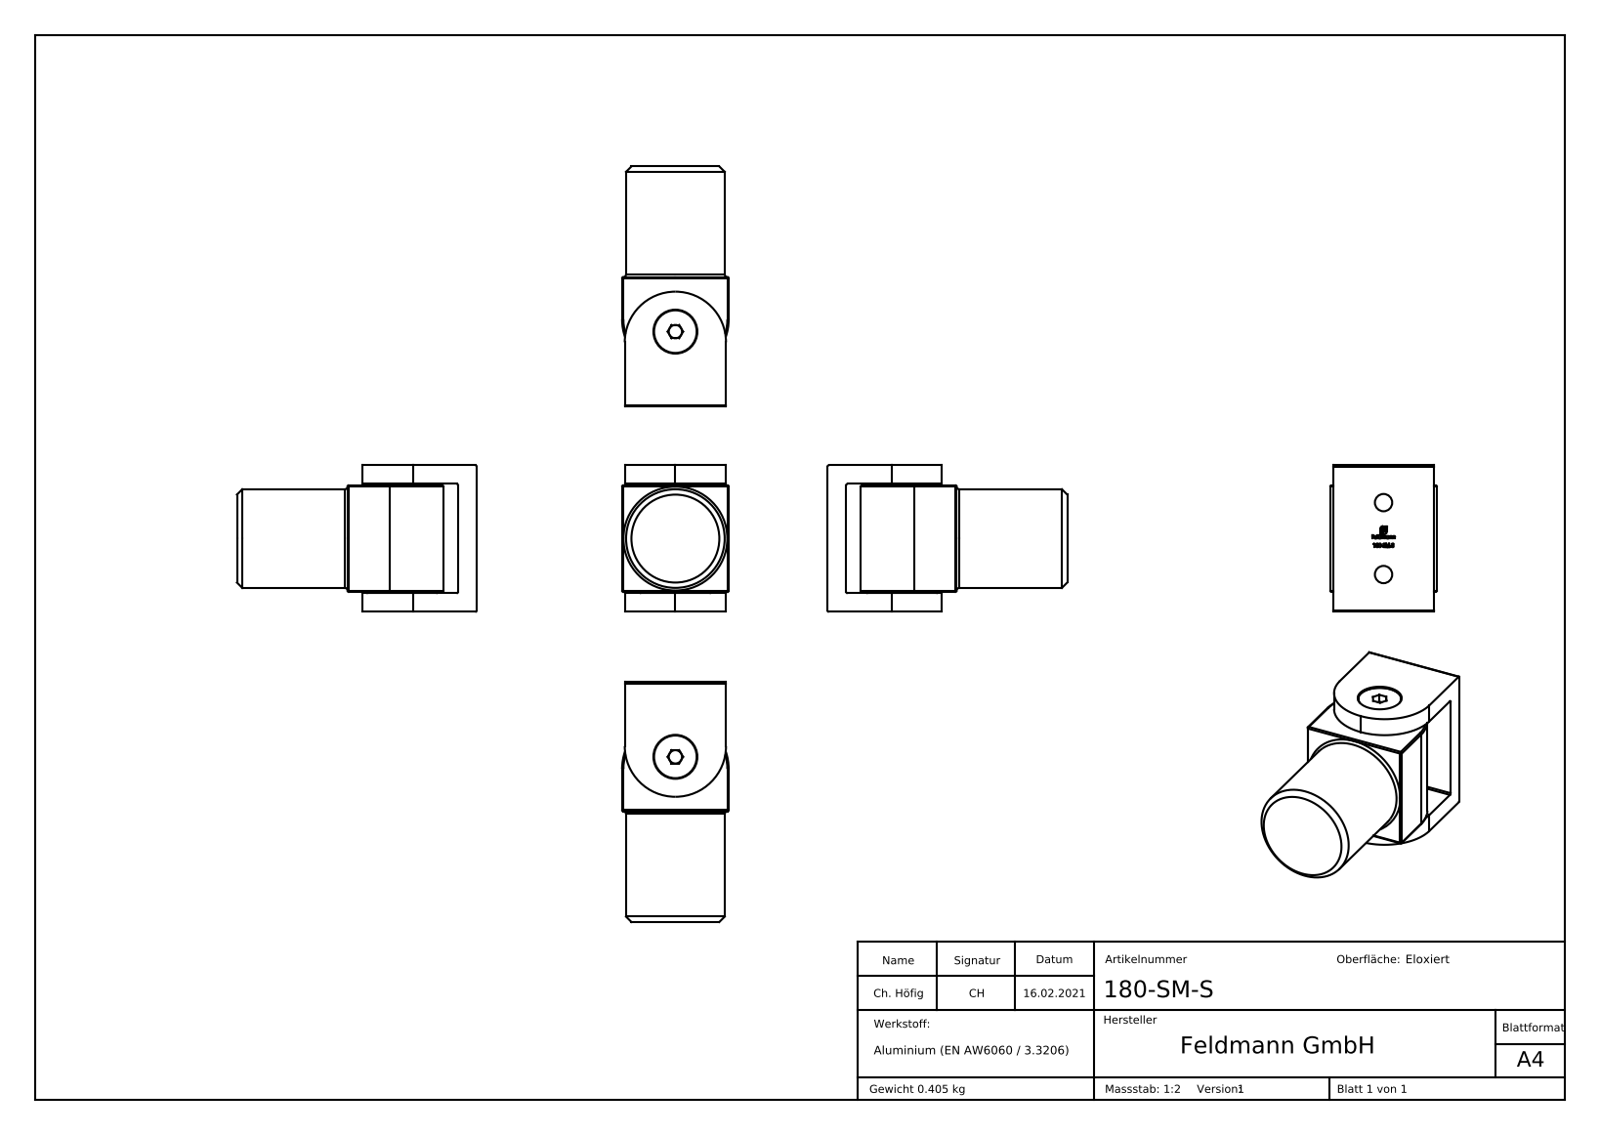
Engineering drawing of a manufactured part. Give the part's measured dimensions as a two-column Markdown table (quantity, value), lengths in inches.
| quantity | value |
| --- | --- |
| part name | Teil4; DIN-7991 M3-M10_DIN7991 M8x18; DIN-7991 M3-M10; 180-SM-S (+7 more) |
| STEP written by | SolidWorks 2018 (CONFIG_CONTROL_DESIGN) |
| units | inches |
| bodies | 11 solids, 511 faces (193 planar, 84 cylindrical, 234 other) |
| overall size | 551.195 × 236.22 × 236.22 |
| volume | 7.654 in³ |
| surface area | 57.08 in² |
| round holes (diameter × count) | 0.256 × 2, 0.492 × 2, 0.268 × 1, 0.335 × 1, 0.65 × 1, 0.748 × 1, 0.929 × 1, 1.024 × 1 |
| round bosses / shafts (diameter × count) | 1.457 × 1, 0.921 × 1, 0.74 × 1, 0.63 × 1, 0.315 × 1 |
| partial cylindrical surfaces (radius × count) | 0.02 × 12, 0.748 × 1, 0.787 × 1 |
| main face-to-face distances | 0.276, 1.89, 1.634, 0.02, 1.614, 0.295, 1.87, 1.594, 0.039, 1.575 |
| hole center spacings | 1.063 |
